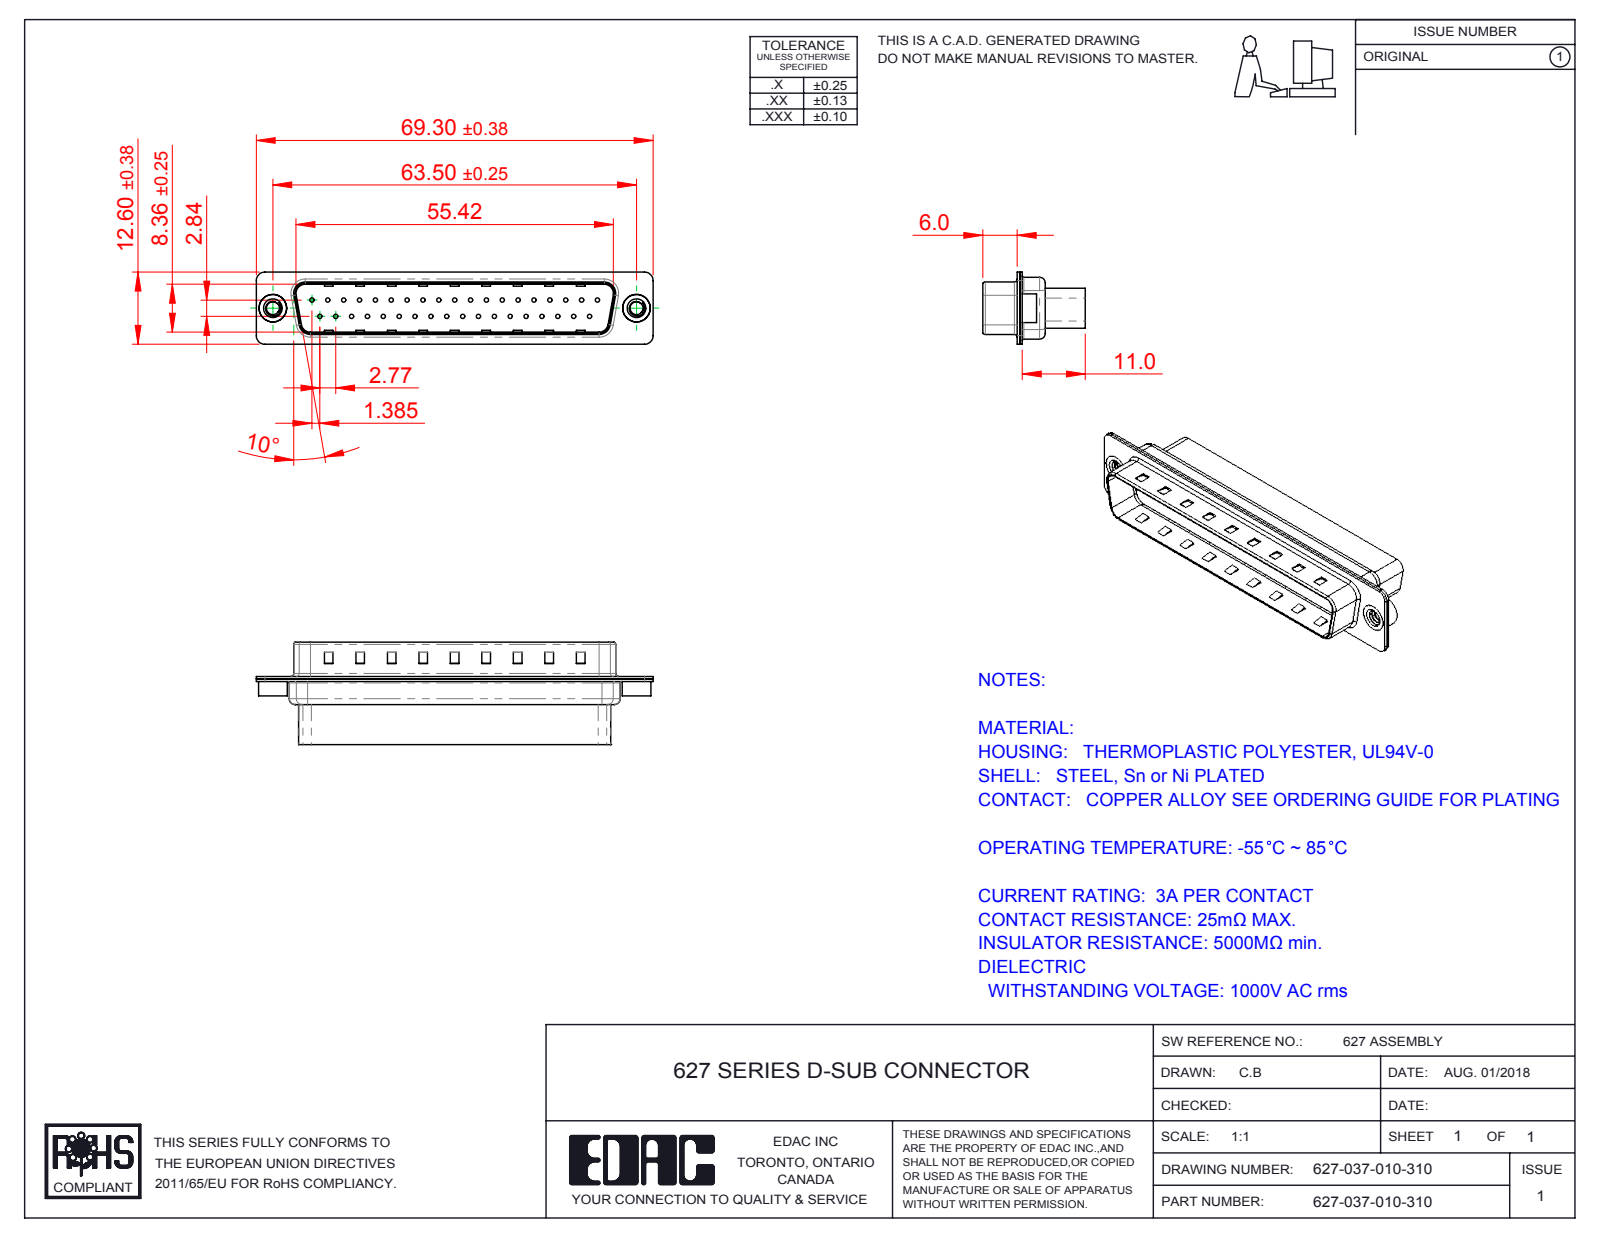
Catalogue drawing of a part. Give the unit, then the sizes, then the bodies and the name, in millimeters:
Units: millimetres
Overall size (bounding box): 69.3 × 17.9 × 12.6
Round holes (diameter × count): ⌀0.75 ×37, ⌀1.6 ×37, ⌀2 ×37, ⌀2.26 ×2, ⌀4 ×2, ⌀4.8 ×2
Round bosses / shafts (diameter × count): ⌀5 ×2, ⌀4.9 ×2
Partial cylindrical surfaces — rounded edges, fillets, slot ends (radius × count): R1.5 ×16, R2 ×12, R0.5 ×8, R1.6 ×8, R0.25 ×4, R0.6 ×4, R0.65 ×4, R0.9 ×4
Main face-to-face distances: 0.4, 0.82, 9.58, 0.68, 7.68, 0.45, 1.08, 8.08, 8.76, 7
Hole centre spacings: 3.16, 2.77, 5.54, 8.31, 5.04, 10.1, 11.08, 12.78
Volume: 5 019 mm³ · Surface area: 9 026 mm²
Bodies: 5 solids, 704 faces (277 planar, 361 cylindrical, 66 other)
Part name (STEP PRODUCT): 627 Housing_37 HP; 627 Shell Front_37 Contacts; 627 4-40 Threaded Rivet; 627-037-010-310 (+1 more)
STEP written by: SolidWorks 2016 (CONFIG_CONTROL_DESIGN)
